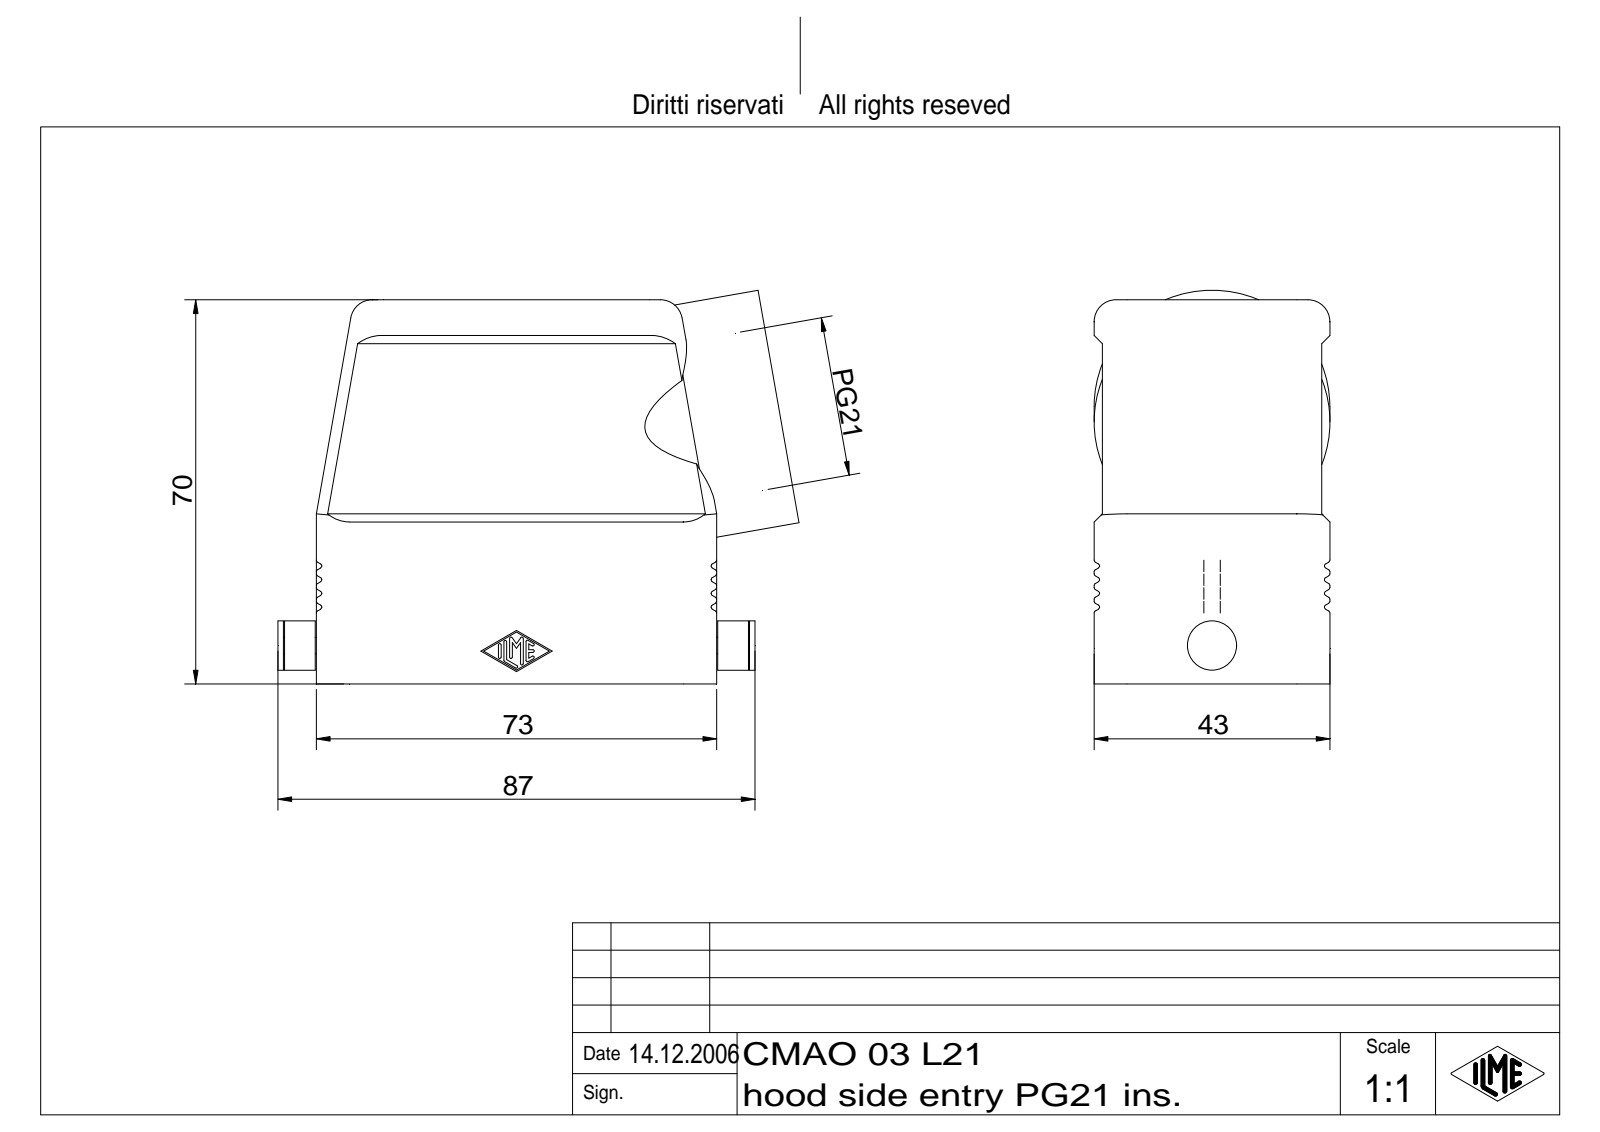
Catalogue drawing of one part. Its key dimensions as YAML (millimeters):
part_name: "CMAO 03 L21"
step_written_by: "Autodesk Inventor 7 (AUTOMOTIVE_DESIGN)"
units: millimeters
bodies: {solids: 1, faces: 661, planar: 135, cylindrical: 318, other: 208}
overall_size: [95.02, 71.74, 43]
volume: 67763
surface_area: 40509
round_holes:
  - {diameter: 25, count: 1}
  - {diameter: 26.78, count: 1}
round_bosses_or_shafts:
  - {diameter: 43, count: 1}
  - {diameter: 9, count: 1}
  - {diameter: 3, count: 1}
partial_cylinders:
  - {radius: 0.4, count: 64}
  - {radius: 0.25, count: 14}
  - {radius: 3, count: 8}
  - {radius: 6, count: 8}
  - {radius: 2, count: 4}
  - {radius: 4, count: 4}
  - {radius: 5, count: 2}
face_to_face_distances: [1.5, 3, 40, 38.5, 37, 41.5, 70, 67, 43, 8.5]
